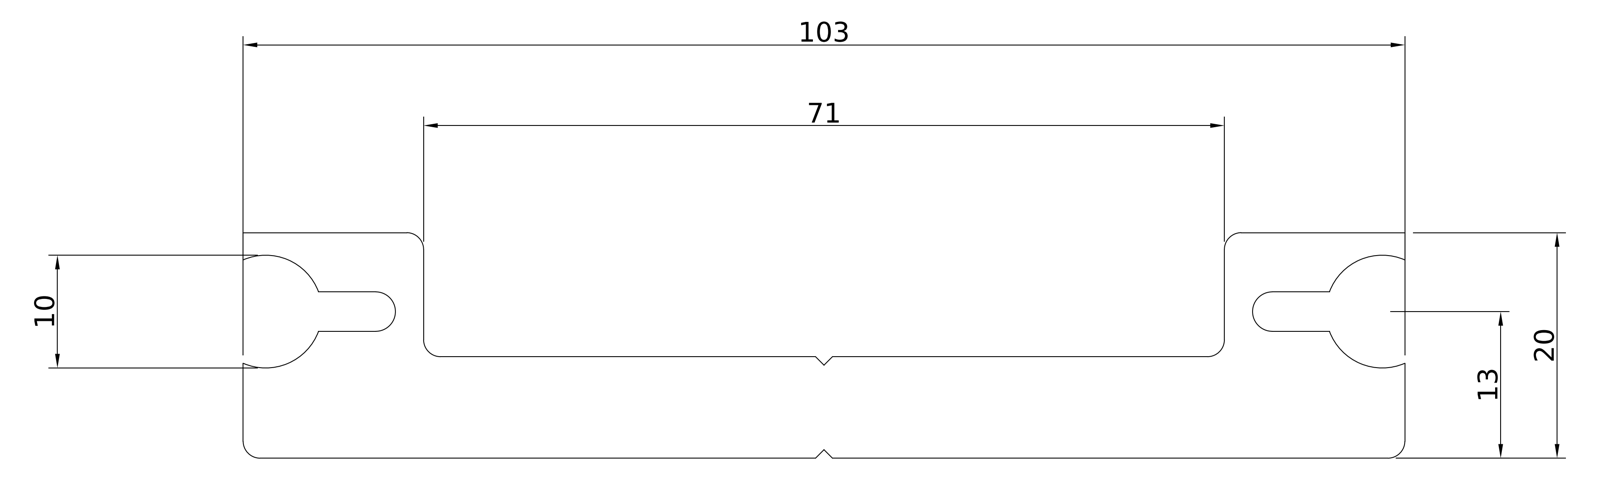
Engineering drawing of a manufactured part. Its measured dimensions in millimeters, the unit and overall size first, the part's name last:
Units: millimetres
Overall size (bounding box): 103 × 100 × 20
Partial cylindrical surfaces — rounded edges, fillets, slot ends (radius × count): R1.5 ×6, R1.75 ×2, R5 ×2
Main face-to-face distances: 9, 20, 11, 16, 87, 100, 11.25, 14.75, 2.25, 5.75
Volume: 111 586 mm³ · Surface area: 33 312 mm²
Bodies: 1 solid, 34 faces (22 planar, 12 cylindrical, 0 other)
Part name (STEP PRODUCT): F3DTM0000606; 3DSD000934
STEP written by: Autodesk Inventor 2022 (AUTOMOTIVE_DESIGN)
